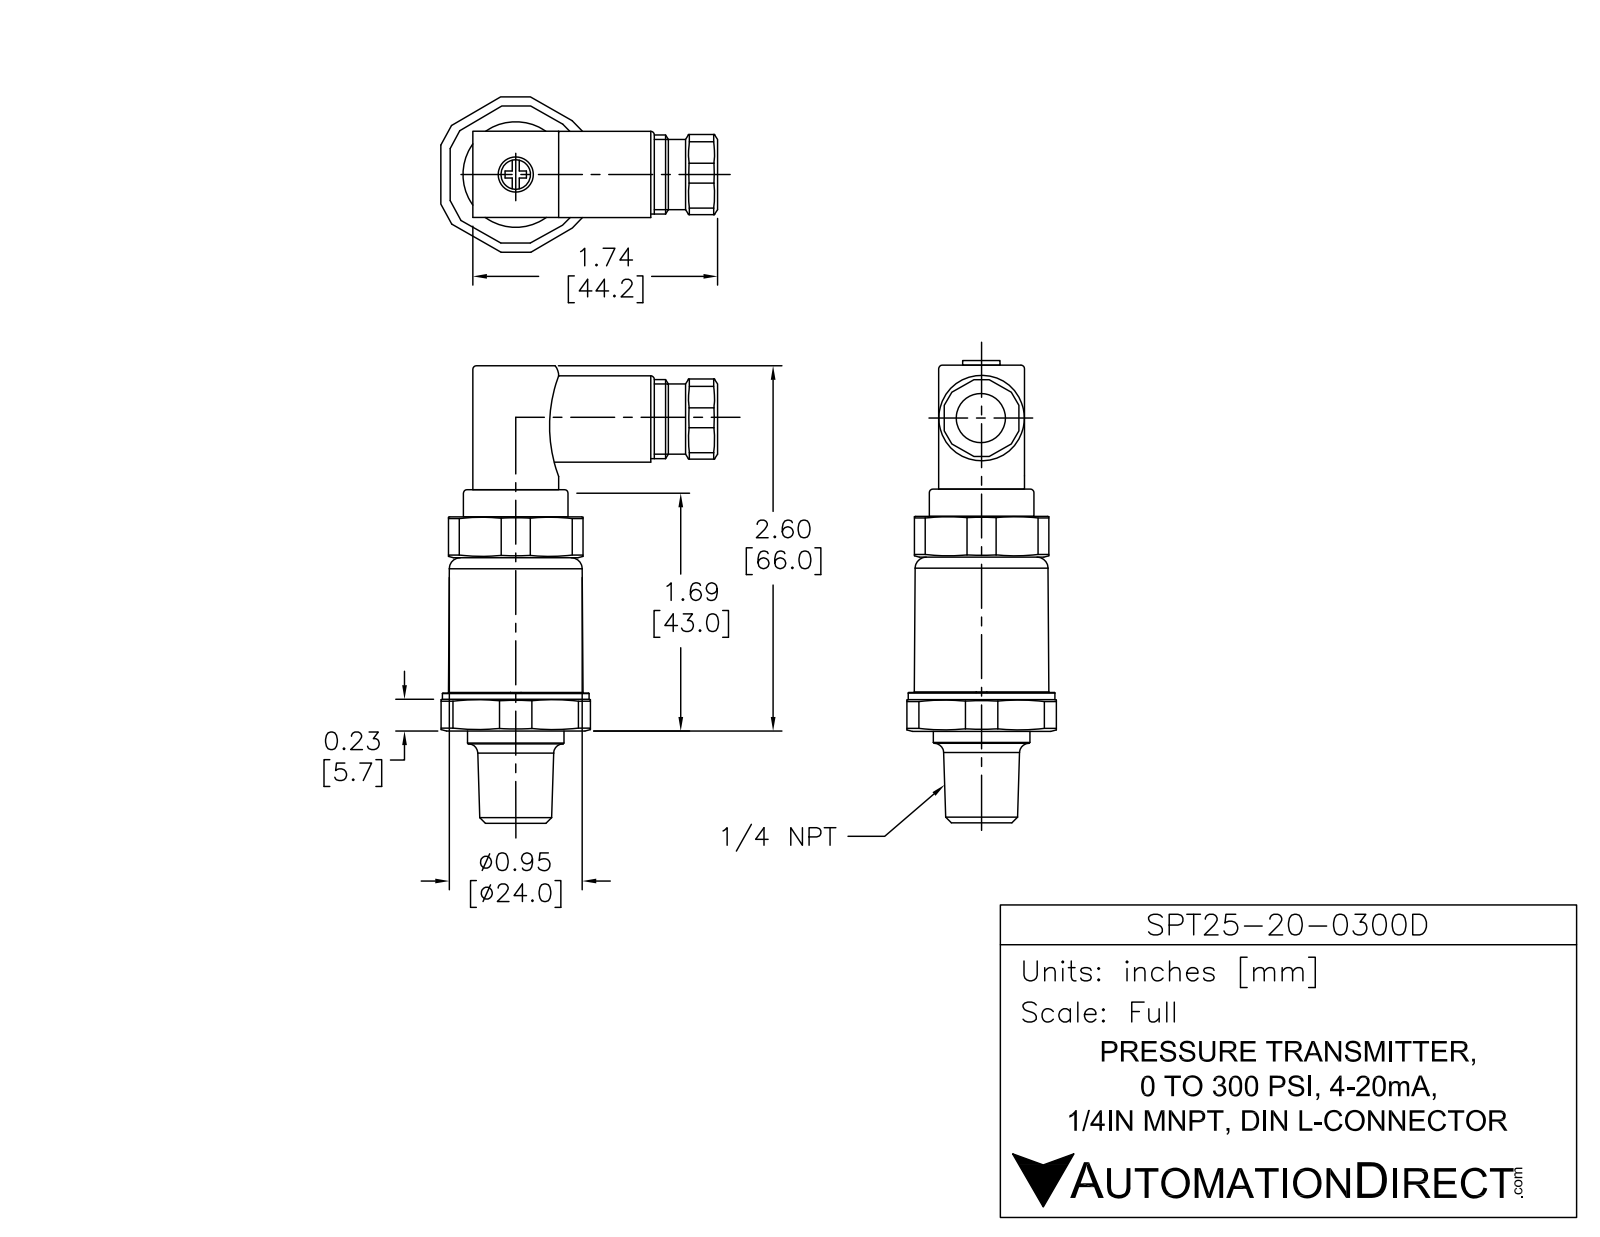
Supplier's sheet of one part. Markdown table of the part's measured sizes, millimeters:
| quantity | value |
| --- | --- |
| part name | SPT25-20-0300D |
| STEP written by | SolidWorks 2013 (AUTOMOTIVE_DESIGN) |
| units | millimeters |
| bodies | 5 solids, 200 faces (96 planar, 87 cylindrical, 17 other) |
| overall size | 81.25 × 38.01 × 35.71 |
| volume | 27 893 mm³ |
| surface area | 10 133 mm² |
| round holes (diameter × count) | 1 × 1, 3.3 × 1, 7 × 1, 8 × 1 |
| round bosses / shafts (diameter × count) | 26.75 × 1, 24 × 1, 17.5 × 1, 15 × 1, 14 × 1, 11 × 1 |
| partial cylindrical surfaces (radius × count) | 1.5 × 8, 1.15 × 4, 2.25 × 4, 2 × 3, 1.15 × 1, 1.17 × 1, 14.5 × 1 |
| main face-to-face distances | 1.5, 29.5, 31, 15.75, 0.35, 15.4, 6.75, 37.75, 36.25, 5 |
| hole center spacings | 1.33 |
